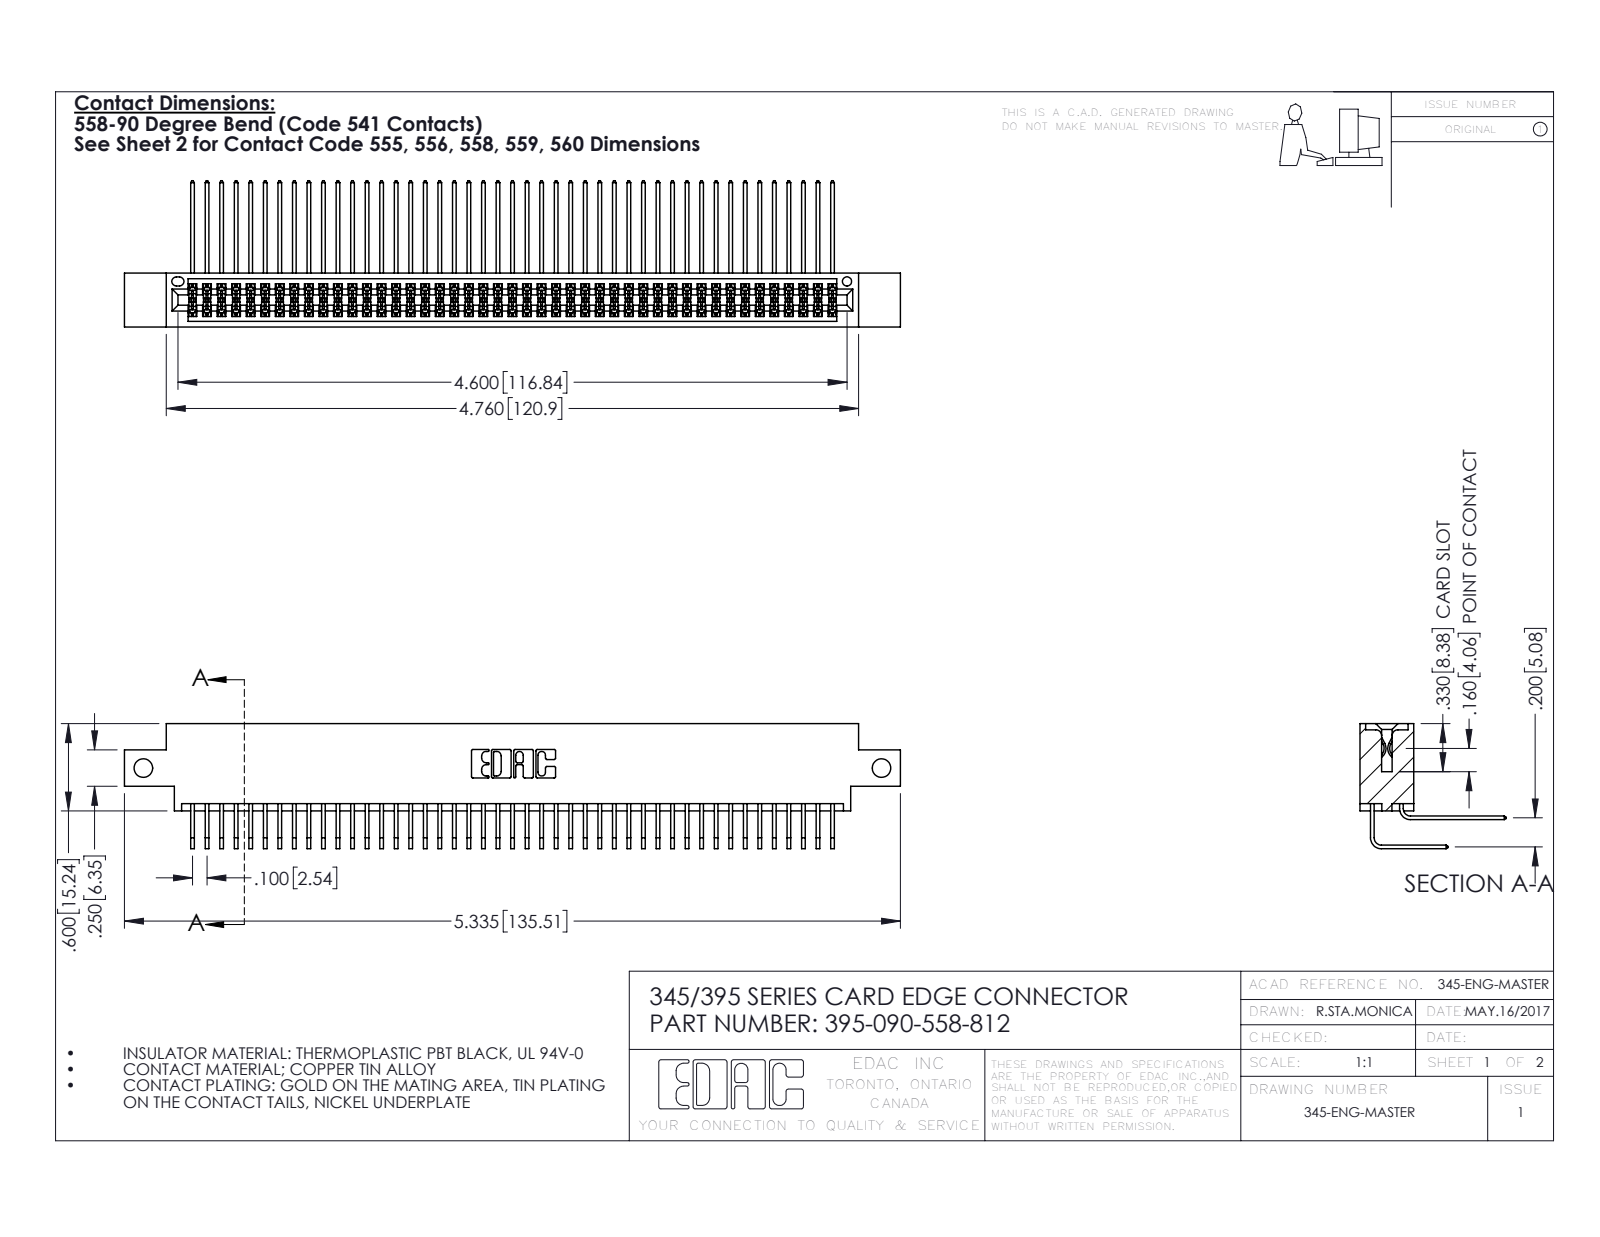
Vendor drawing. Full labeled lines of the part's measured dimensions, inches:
Part name (STEP PRODUCT): 345-292-001_558 559 Tail - 1; 345-292-001_558 Tail - 2; 395-090-558-812; 345 Part_0.170 Offset - Side Mount
STEP written by: SolidWorks 2016 (CONFIG_CONTROL_DESIGN)
Units: inches
Bodies: 91 solids, 4810 faces (3234 planar, 1576 cylindrical, 0 other)
Overall size (bounding box): 5.335 × 1.005 × 0.859
Volume: 0.824 in³ · Surface area: 34.84 in²
Round holes (diameter × count): ⌀0.128 ×2, ⌀0.064 ×1
Partial cylindrical surfaces — rounded edges, fillets, slot ends (radius × count): R0.006 ×136, R0.01 ×22, R0.007 ×6, R0.031 ×6, R0.026 ×3, R0.014 ×2, R0.019 ×2, R0.022 ×2
Main face-to-face distances: 0.072, 0.298, 0.2, 0.37, 0.098, 0.272, 0.025, 0.225, 0.175, 0.025
Hole centre spacings: 5.075
